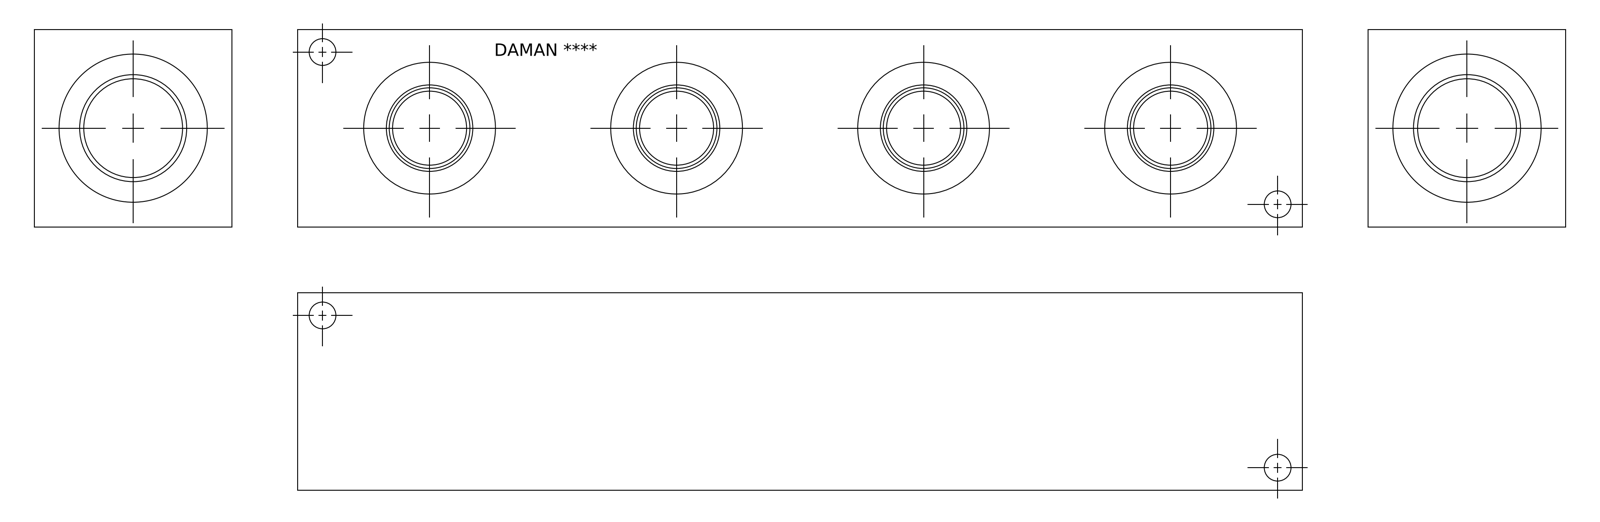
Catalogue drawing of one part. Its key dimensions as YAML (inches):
part_name: "Part_DH0000416S_3D"
step_written_by: "Autodesk Inventor 2019 (AUTOMOTIVE_DESIGN)"
units: inches
bodies: {solids: 1, faces: 383, planar: 229, cylindrical: 38, other: 116}
overall_size: [15.25, 3, 3]
volume: 123.6
surface_area: 246
round_holes:
  - {diameter: 0.406, count: 4}
  - {diameter: 1.125, count: 4}
  - {diameter: 1.231, count: 4}
  - {diameter: 1.313, count: 4}
  - {diameter: 1.329, count: 4}
  - {diameter: 1.934, count: 4}
  - {diameter: 1.5, count: 1}
  - {diameter: 1.544, count: 1}
  - {diameter: 1.625, count: 1}
  - {diameter: 1.625, count: 1}
  - {diameter: 1.644, count: 1}
  - {diameter: 1.713, count: 1}
face_to_face_distances: [3, 0.031, 2.969, 15.25, 15.219, 15.188, 0.781, 0.75, 2.219, 14.469]
hole_center_spacings: [3.75, 1.994, 5.498, 7.5, 9.198, 12.927, 14.683, 11.25]
